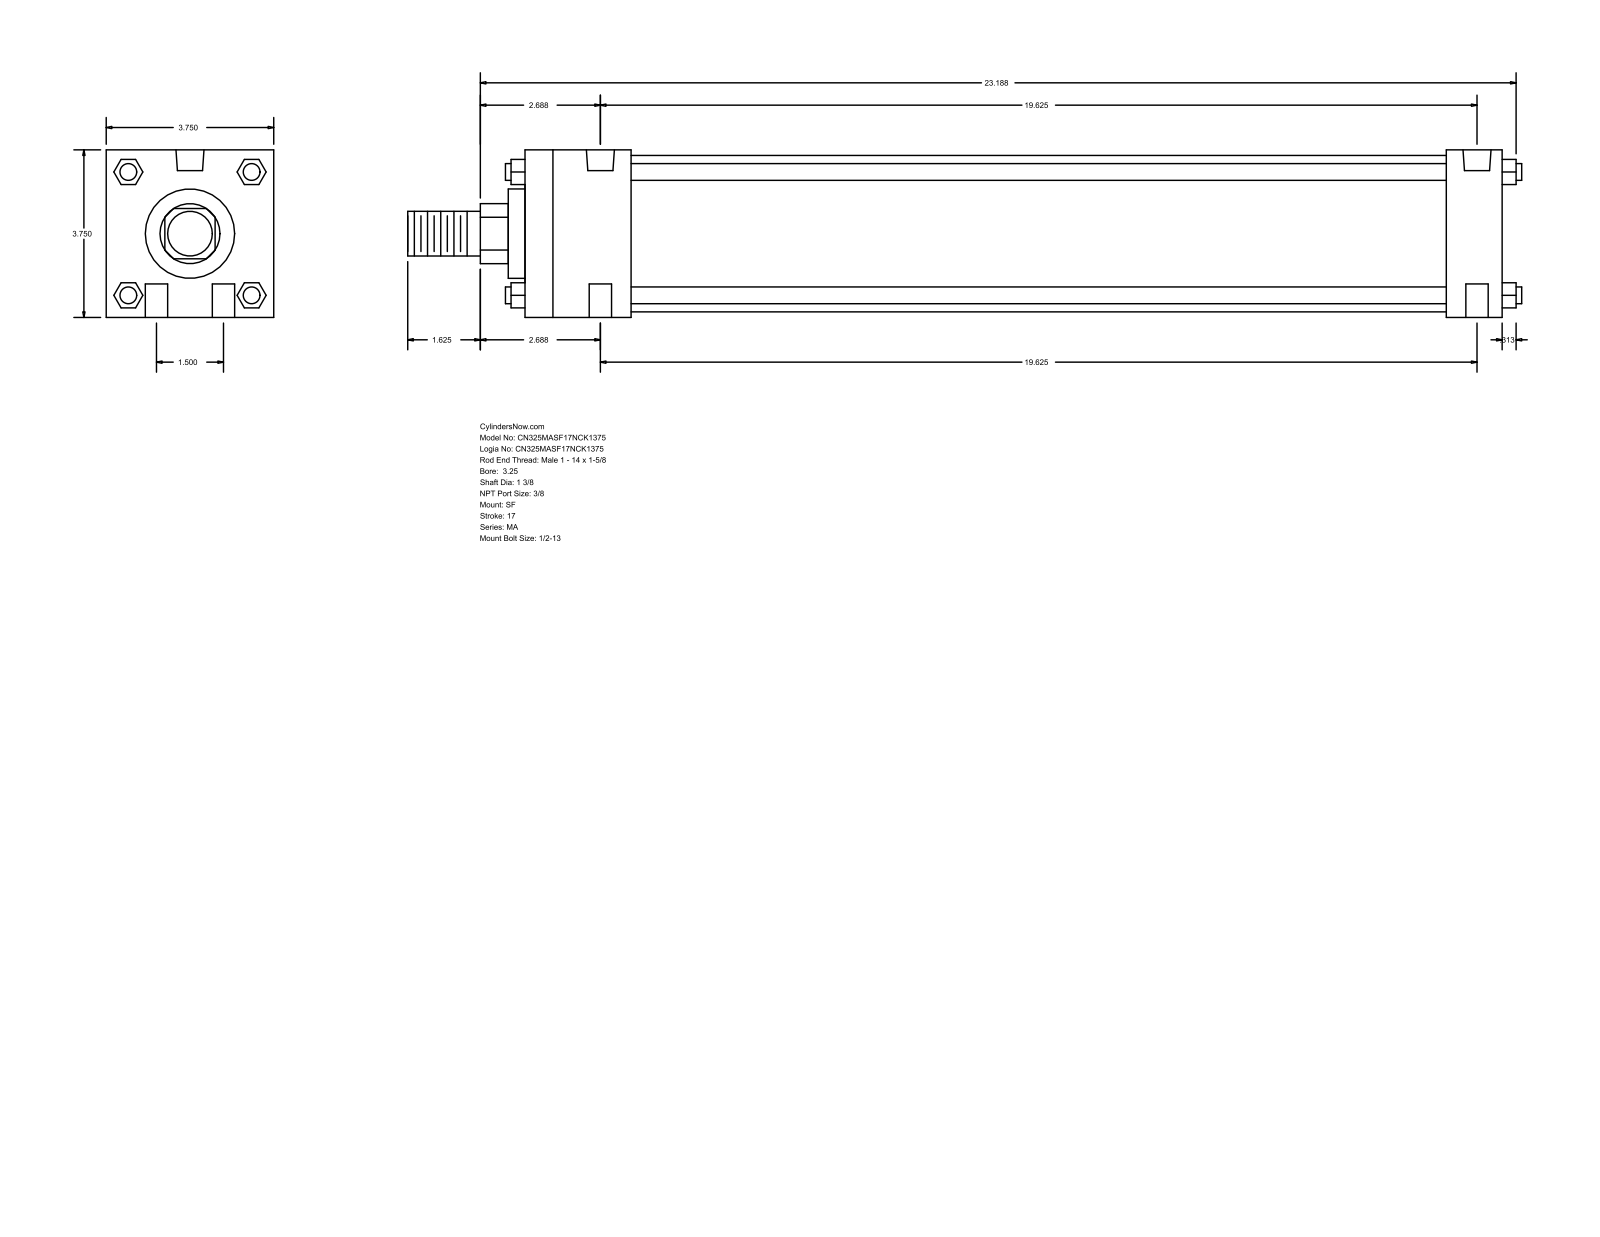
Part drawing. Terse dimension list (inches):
name: MA_SF__0325_1.375
written by: GSSL Pune (CONFIG_CONTROL_DESIGN)
unit: in
bodies: 0 solids, 124 faces (94 planar, 30 cylindrical, 0 other)
size: 24.937 × 3.75 × 3.75
holes: 4× ⌀0.5, 2× ⌀0.437, 2× ⌀0.627
bosses: 4× ⌀0.375, 1× ⌀3.5, 1× ⌀2, 1× ⌀1.375, 1× ⌀1
rounds: 1× R0.672
face distances: 3.75, 21.875, 20.625, 1.25, 2.375, 18.25, 19.5, 0.375, 2.75, 21
hole spacings: 0.75, 19.639, 19.625, 1.5, 19.682, 19.25
